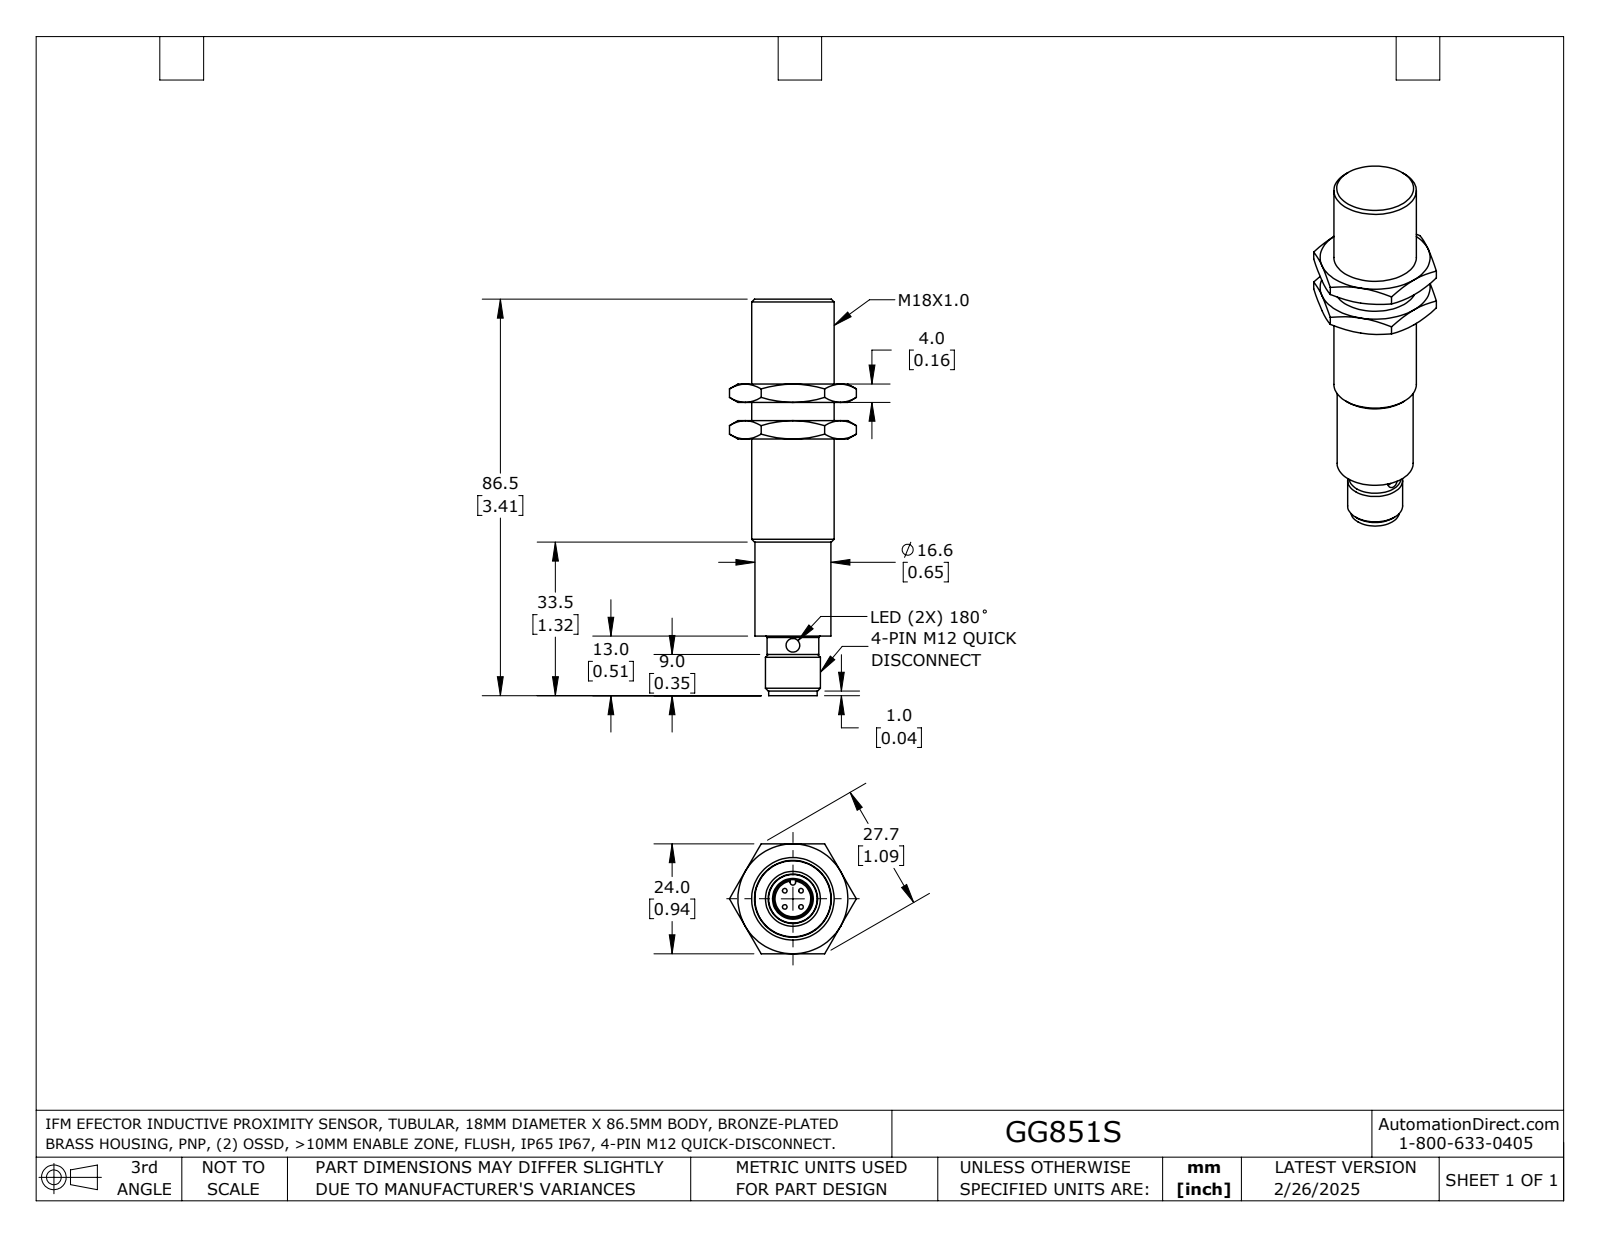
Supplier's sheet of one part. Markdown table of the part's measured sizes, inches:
| quantity | value |
| --- | --- |
| part name | GG851S |
| STEP written by | SolidWorks 2024 (AUTOMOTIVE_DESIGN) |
| units | inches |
| bodies | 3 solids, 74 faces (26 planar, 11 cylindrical, 37 other) |
| overall size | 3.406 × 1.091 × 0.945 |
| volume | 1.274 in³ |
| surface area | 11.34 in² |
| round holes (diameter × count) | 0.118 × 1, 0.331 × 1, 0.666 × 1 |
| round bosses / shafts (diameter × count) | 0.709 × 1, 0.654 × 1, 0.472 × 1, 0.445 × 1, 0.417 × 1 |
| partial cylindrical surfaces (radius × count) | 0.024 × 1 |
| main face-to-face distances | 0.157, 0.315, 0.945, 0.886, 1.201, 1.043, 0.472, 0.728, 2.165, 2.008 |
